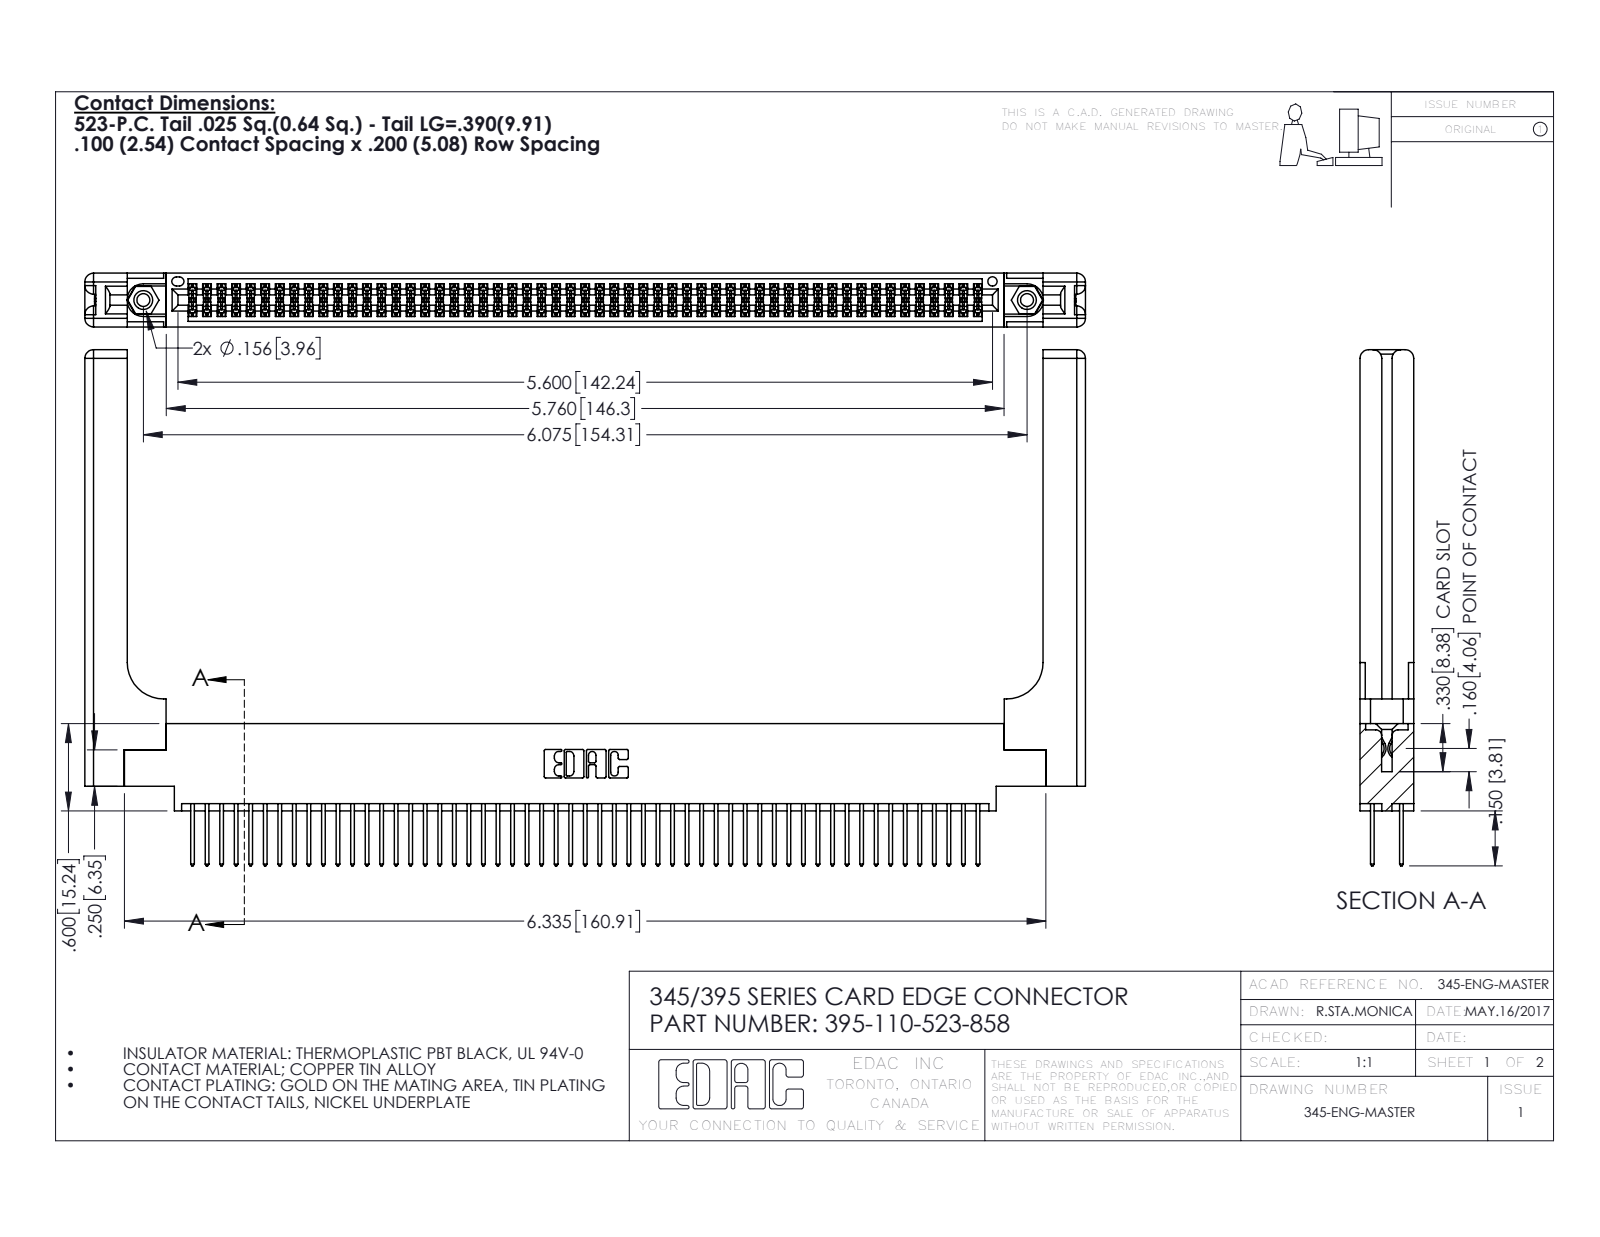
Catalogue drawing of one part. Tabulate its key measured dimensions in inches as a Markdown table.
| quantity | value |
| --- | --- |
| part name | 395-110-523-858; 345 Part_0.170 Offset - 0.156 Dia-TH; 345-220-058_345-220-058; 345-292-001_345-293-123 (+1 more) |
| STEP written by | SolidWorks 2016 (CONFIG_CONTROL_DESIGN) |
| units | inches |
| bodies | 115 solids, 5886 faces (3862 planar, 1964 cylindrical, 60 other) |
| overall size | 6.879 × 3.547 × 0.37 |
| volume | 1.567 in³ |
| surface area | 49.44 in² |
| round holes (diameter × count) | 0.089 × 2, 0.125 × 2, 0.156 × 2, 0.064 × 1 |
| round bosses / shafts (diameter × count) | 0.155 × 2 |
| partial cylindrical surfaces (radius × count) | 0.006 × 165, 0.01 × 110, 0.01 × 22, 0.06 × 16, 0.007 × 6, 0.031 × 6, 0.026 × 3, 0.014 × 2 |
| main face-to-face distances | 0.072, 0.298, 0.37, 0.098, 0.272, 0.025, 0.2, 0.225, 0.175, 0.148 |
| hole center spacings | 0.27, 5.839, 6.075 |
